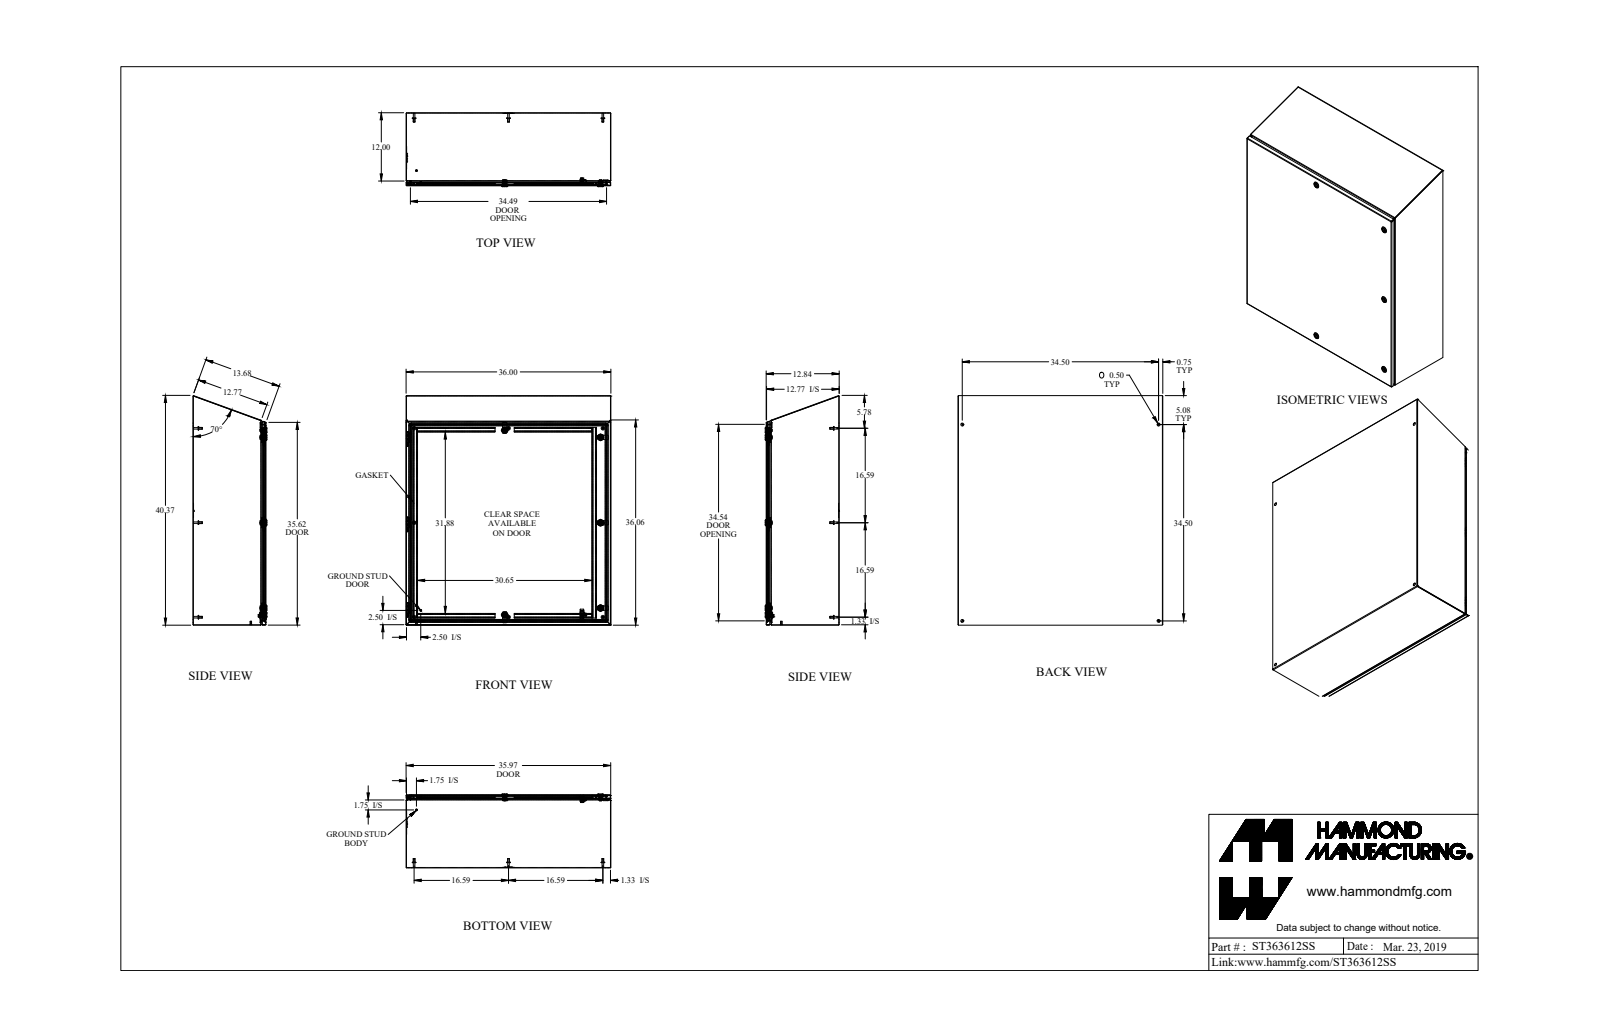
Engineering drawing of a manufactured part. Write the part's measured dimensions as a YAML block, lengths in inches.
part_name: "ST363612SS"
step_written_by: "SolidWorks 2018 (AUTOMOTIVE_DESIGN)"
units: inches
bodies: {solids: 62, faces: 1594, planar: 844, cylindrical: 509, other: 241}
overall_size: [40.328, 36, 12.997]
volume: 372.8
surface_area: 10500
round_holes:
  - {diameter: 0.5, count: 9}
  - {diameter: 0.197, count: 5}
  - {diameter: 0.387, count: 5}
  - {diameter: 0.63, count: 5}
  - {diameter: 0.768, count: 5}
  - {diameter: 0.172, count: 1}
  - {diameter: 0.196, count: 1}
  - {diameter: 0.24, count: 1}
  - {diameter: 0.242, count: 1}
  - {diameter: 0.275, count: 1}
  - {diameter: 0.375, count: 1}
round_bosses_or_shafts:
  - {diameter: 0.625, count: 12}
  - {diameter: 0.313, count: 10}
  - {diameter: 0.275, count: 8}
  - {diameter: 1.1, count: 5}
  - {diameter: 0.785, count: 5}
  - {diameter: 0.525, count: 5}
  - {diameter: 0.236, count: 5}
  - {diameter: 0.625, count: 2}
partial_cylinders:
  - {radius: 0.01, count: 30}
  - {radius: 0.048, count: 30}
  - {radius: 0.036, count: 18}
  - {radius: 0.108, count: 18}
  - {radius: 0.062, count: 10}
  - {radius: 0.094, count: 10}
  - {radius: 0.125, count: 10}
  - {radius: 0.016, count: 9}
face_to_face_distances: [0.072, 12.765, 12.693, 12.837, 35.928, 35.856, 36, 11.928, 0.837, 0.038]
hole_center_spacings: [34.5, 15, 33.503, 48.791, 2.492, 2.494, 3.542, 4.442]
